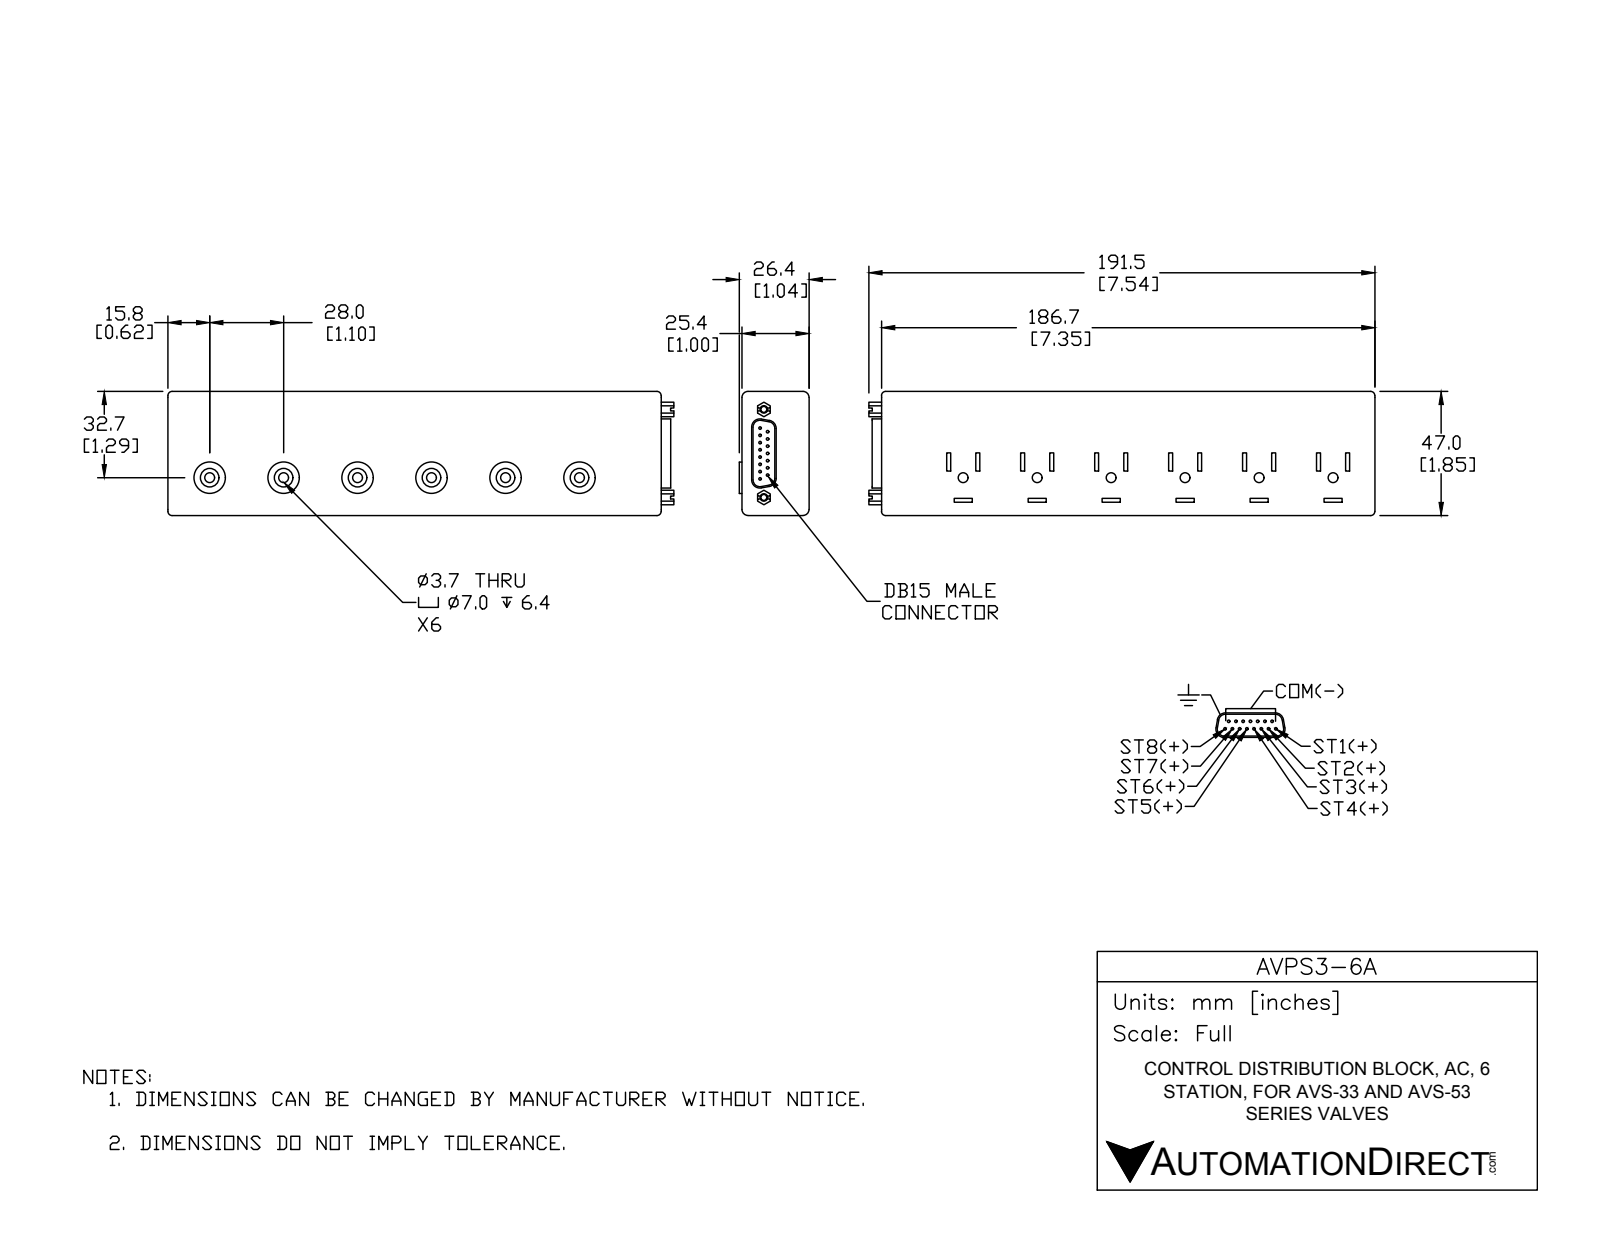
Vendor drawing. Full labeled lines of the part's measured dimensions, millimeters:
Part name (STEP PRODUCT): AVPS3-6A
STEP written by: SolidWorks 2016 (AUTOMOTIVE_DESIGN)
Units: millimetres
Bodies: 1 solid, 265 faces (161 planar, 92 cylindrical, 12 other)
Overall size (bounding box): 191.5 × 47 × 26.4
Volume: 218 300 mm³ · Surface area: 33 850 mm²
Round holes (diameter × count): ⌀3.7 ×6, ⌀7 ×6, ⌀2.3 ×2
Round bosses / shafts (diameter × count): ⌀1 ×15, ⌀11.9 ×6
Partial cylindrical surfaces — rounded edges, fillets, slot ends (radius × count): R1.6 ×7, R2.3 ×4, R2.6 ×4, R3.1 ×4, R1.6 ×1
Main face-to-face distances: 25.4, 47, 186.7, 28, 1.5, 1, 26.4, 6.4, 20.1, 56
Hole centre spacings: 28, 56, 56, 84, 112, 28, 33.3, 84
